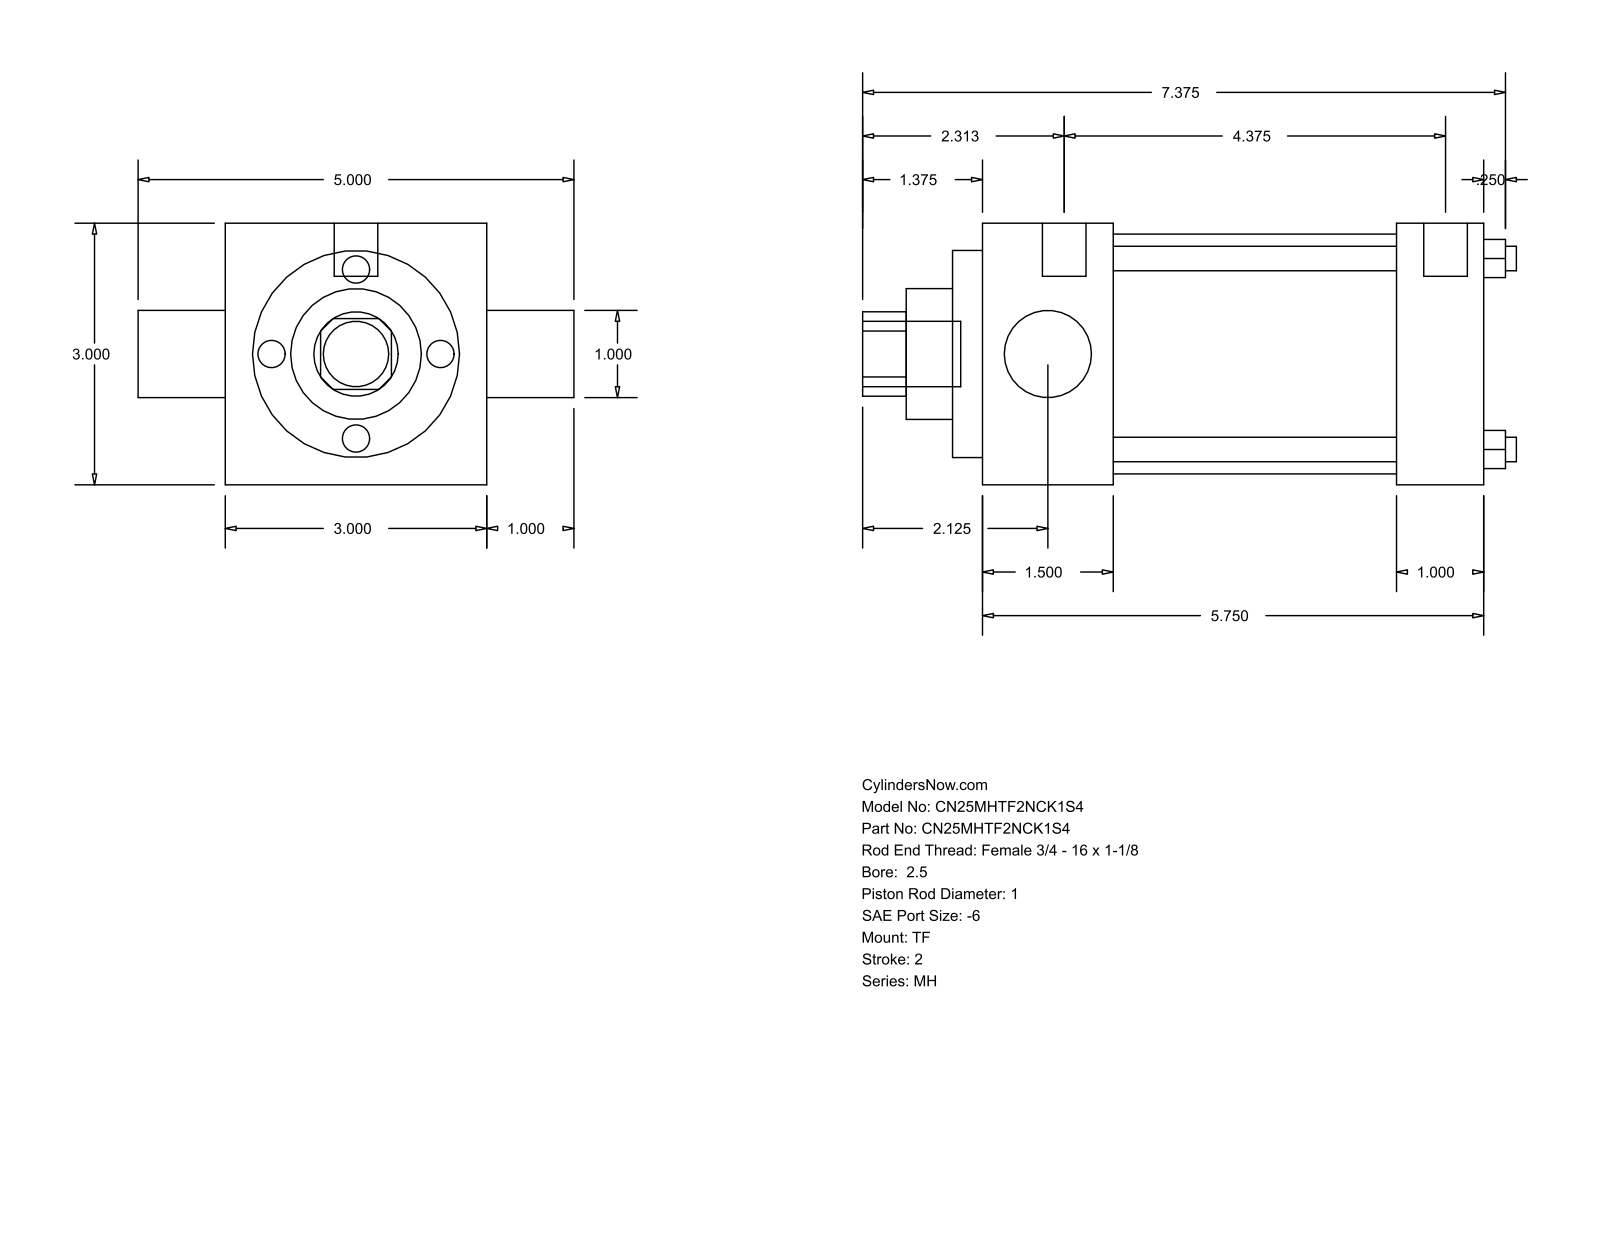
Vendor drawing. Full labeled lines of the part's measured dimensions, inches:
Part name (STEP PRODUCT): MH_TF__0250_1
STEP written by: GSSL Pune (CONFIG_CONTROL_DESIGN)
Units: inches
Bodies: 0 solids, 86 faces (61 planar, 25 cylindrical, 0 other)
Overall size (bounding box): 7.5 × 5 × 3
Round holes (diameter × count): ⌀0.281 ×4, ⌀1 ×2, ⌀1.5 ×1, ⌀2.375 ×1, ⌀2.75 ×1
Round bosses / shafts (diameter × count): ⌀0.219 ×3, ⌀0.5 ×2, ⌀0.75 ×1
Partial cylindrical surfaces — rounded edges, fillets, slot ends (radius × count): R0.484 ×1
Main face-to-face distances: 3, 5.75, 1, 1.5, 4.25, 4.75, 3.25, 0.344, 1.844, 5.094
Hole centre spacings: 1.548, 2.19, 3.097
